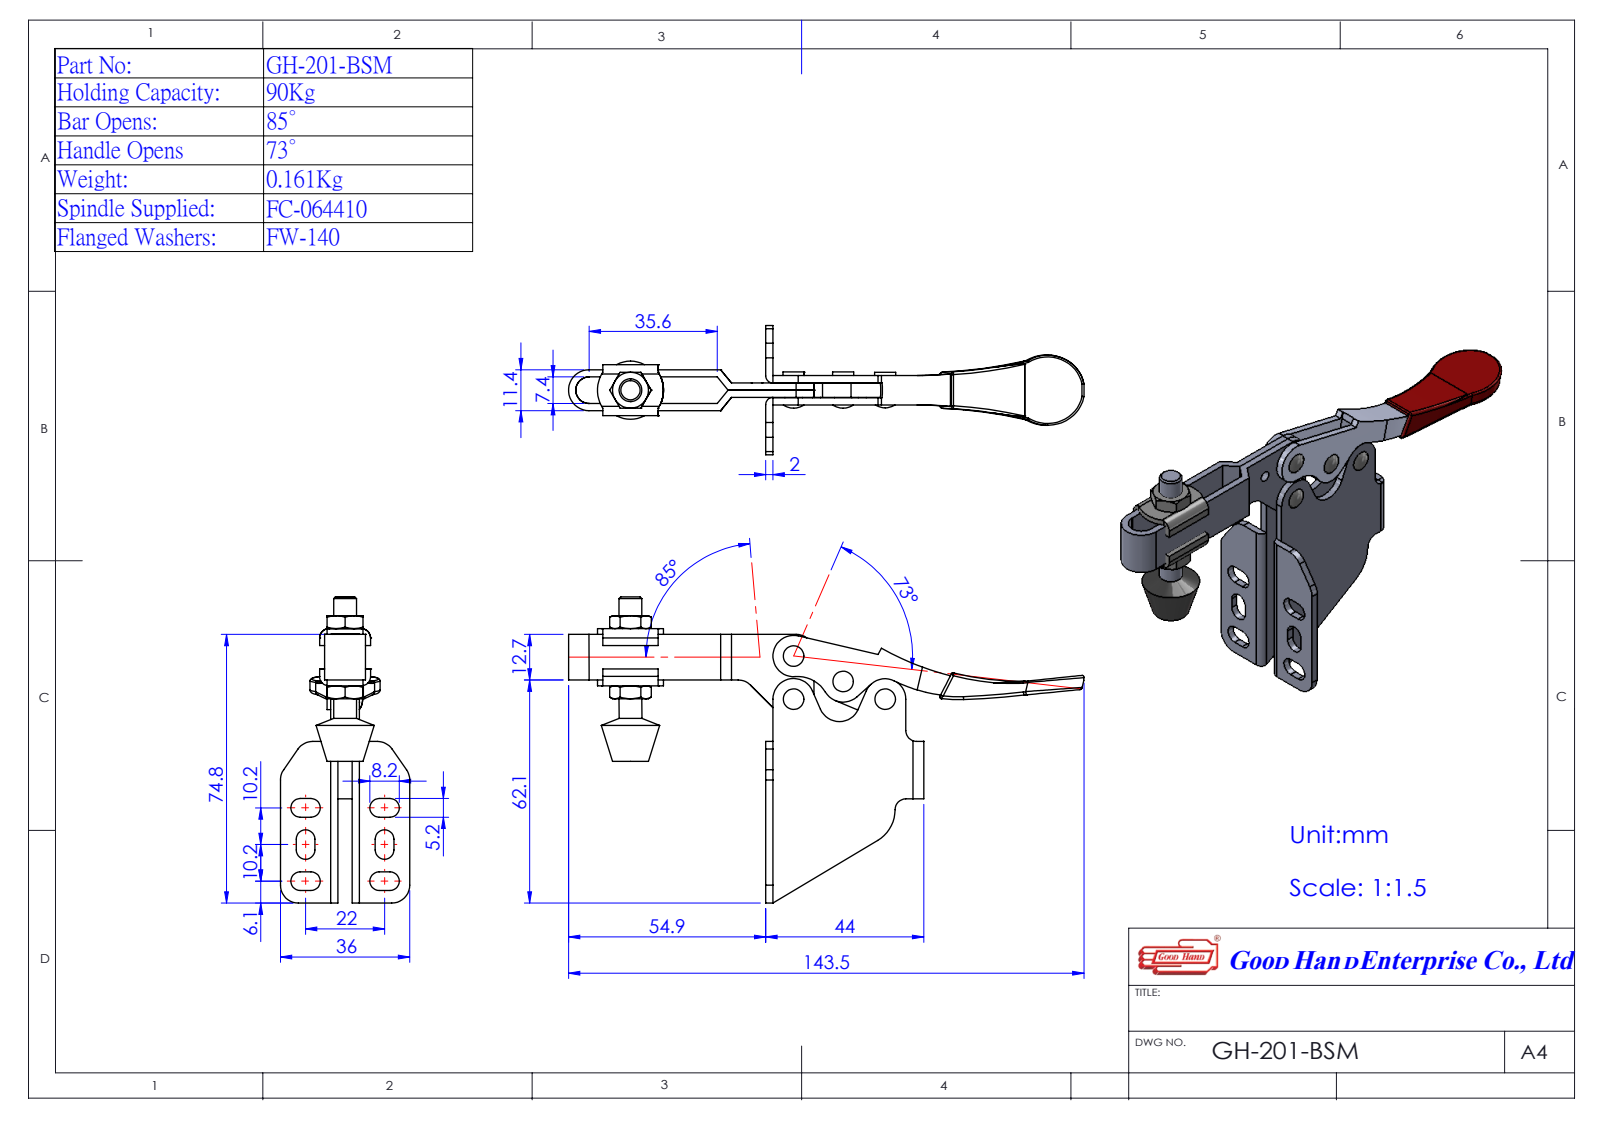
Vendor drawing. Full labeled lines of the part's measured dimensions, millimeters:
Part name (STEP PRODUCT): Group5^GH-201-BSM(簡化)-1; 1201B05-1^GH-201-BSM(簡化)-1; GH-201-BSM(簡化)-1; Group1^GH-201-BSM(簡化) (+2 more)
STEP written by: SolidWorks 2016 (AUTOMOTIVE_DESIGN)
Units: millimetres
Bodies: 5 solids, 283 faces (130 planar, 128 cylindrical, 25 other)
Overall size (bounding box): 143.52 × 84.48 × 36
Volume: 24 574 mm³ · Surface area: 23 571 mm²
Round holes (diameter × count): ⌀3.5 ×2, ⌀4 ×2
Round bosses / shafts (diameter × count): ⌀5.85 ×4, ⌀4.85 ×2, ⌀3.5 ×2, ⌀6.35 ×1
Partial cylindrical surfaces — rounded edges, fillets, slot ends (radius × count): R2.6 ×16, R5 ×8, R5.75 ×6, R1 ×4, R80 ×3, R3 ×2, R5.7 ×2, R78.5 ×2
Main face-to-face distances: 2, 4, 6, 8, 1.7, 3.7, 5.7, 7.7, 1.6, 7.8
Hole centre spacings: 12, 12.7, 14.64, 15.5, 25.5, 28.18
